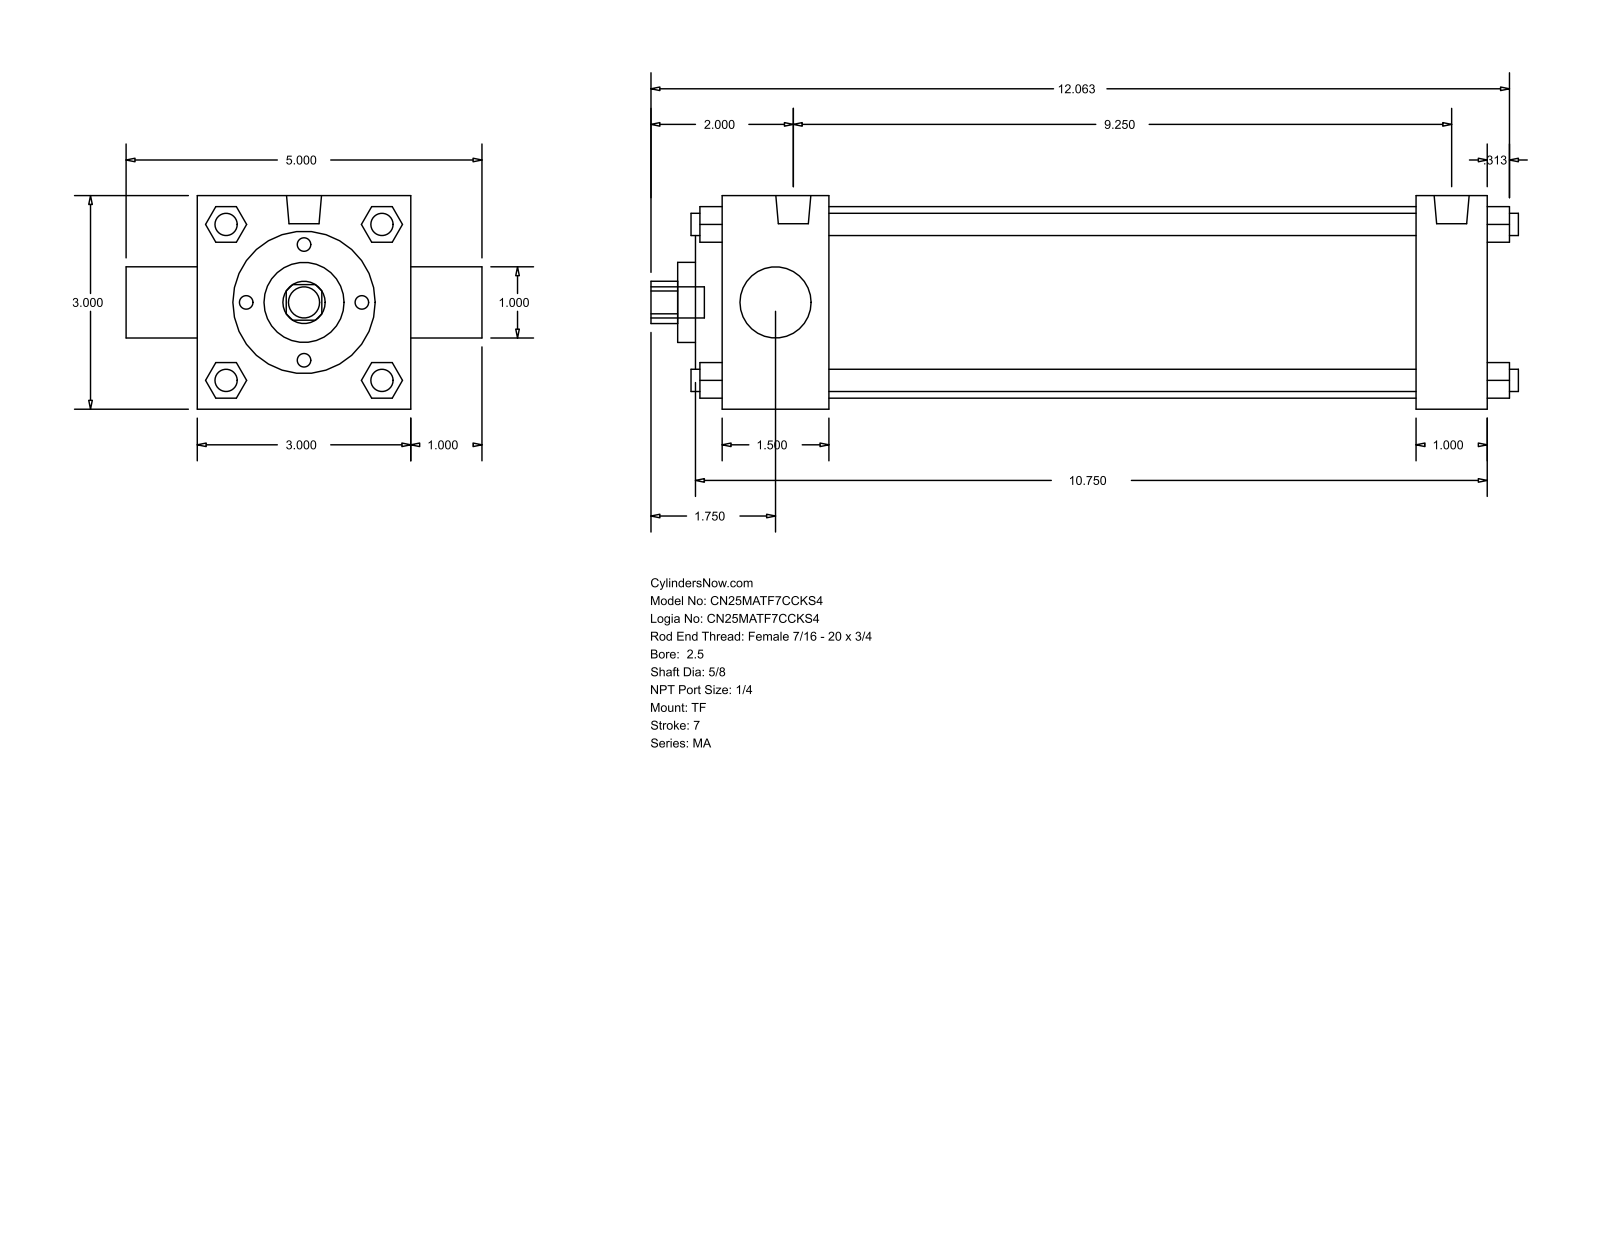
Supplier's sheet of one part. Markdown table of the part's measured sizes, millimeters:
| quantity | value |
| --- | --- |
| part name | MA_TF__0250_0.625 |
| STEP written by | GSSL Pune (CONFIG_CONTROL_DESIGN) |
| units | millimeters |
| bodies | 0 solids, 122 faces (93 planar, 29 cylindrical, 0 other) |
| overall size | 309.56 × 127 × 76.2 |
| round holes (diameter × count) | 15.88 × 1, 25.4 × 1, 28.57 × 1, 50.8 × 1, 68.33 × 1 |
| round bosses / shafts (diameter × count) | 7.94 × 7, 12.49 × 2, 11.11 × 1 |
| partial cylindrical surfaces (radius × count) | 7.54 × 1 |
| main face-to-face distances | 76.2, 273.05, 25.4, 38.1, 247.65, 209.55, 234.95, 12.7, 9.52, 47.62 |
